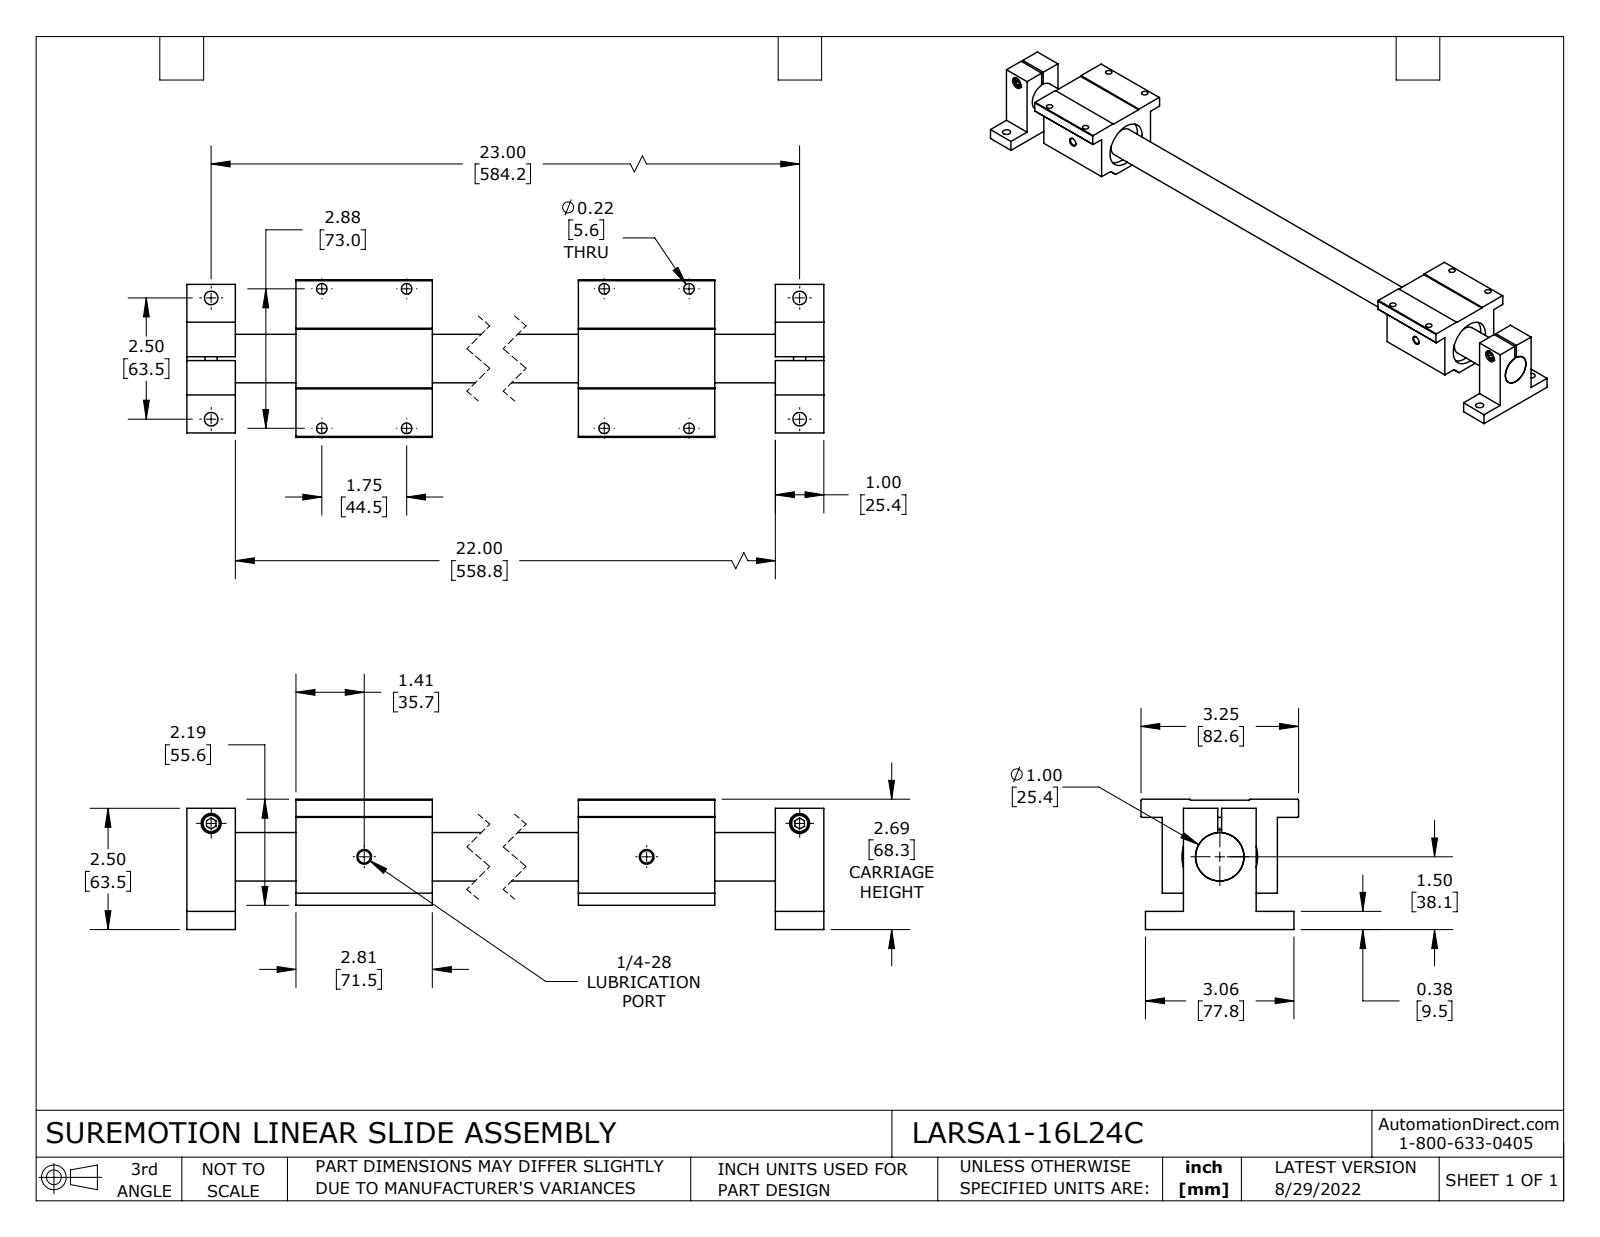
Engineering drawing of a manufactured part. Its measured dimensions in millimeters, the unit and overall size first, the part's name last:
Units: millimetres
Overall size (bounding box): 609.6 × 82.6 × 68.2
Round holes (diameter × count): ⌀5.6 ×8, ⌀7.1 ×4, ⌀6.6 ×2, ⌀10.5 ×2, ⌀25.4 ×1, ⌀39.7 ×1
Round bosses / shafts (diameter × count): ⌀9.5 ×2, ⌀6.4 ×2
Main face-to-face distances: 71.5, 423.8, 60.4, 11.1, 49.2, 9.5, 58.7, 584.2, 25.4, 0.5
Hole centre spacings: 423.8, 44.5, 58.1, 73, 85.5, 89.5, 102.5, 123.1
Volume: 811 200 mm³ · Surface area: 143 500 mm²
Bodies: 7 solids, 166 faces (98 planar, 60 cylindrical, 8 other)
Part name (STEP PRODUCT): LARSA1-16L24C-RAIL; LARSA1-16L24C; LARSACC-003
STEP written by: SolidWorks 2021 (CONFIG_CONTROL_DESIGN)
